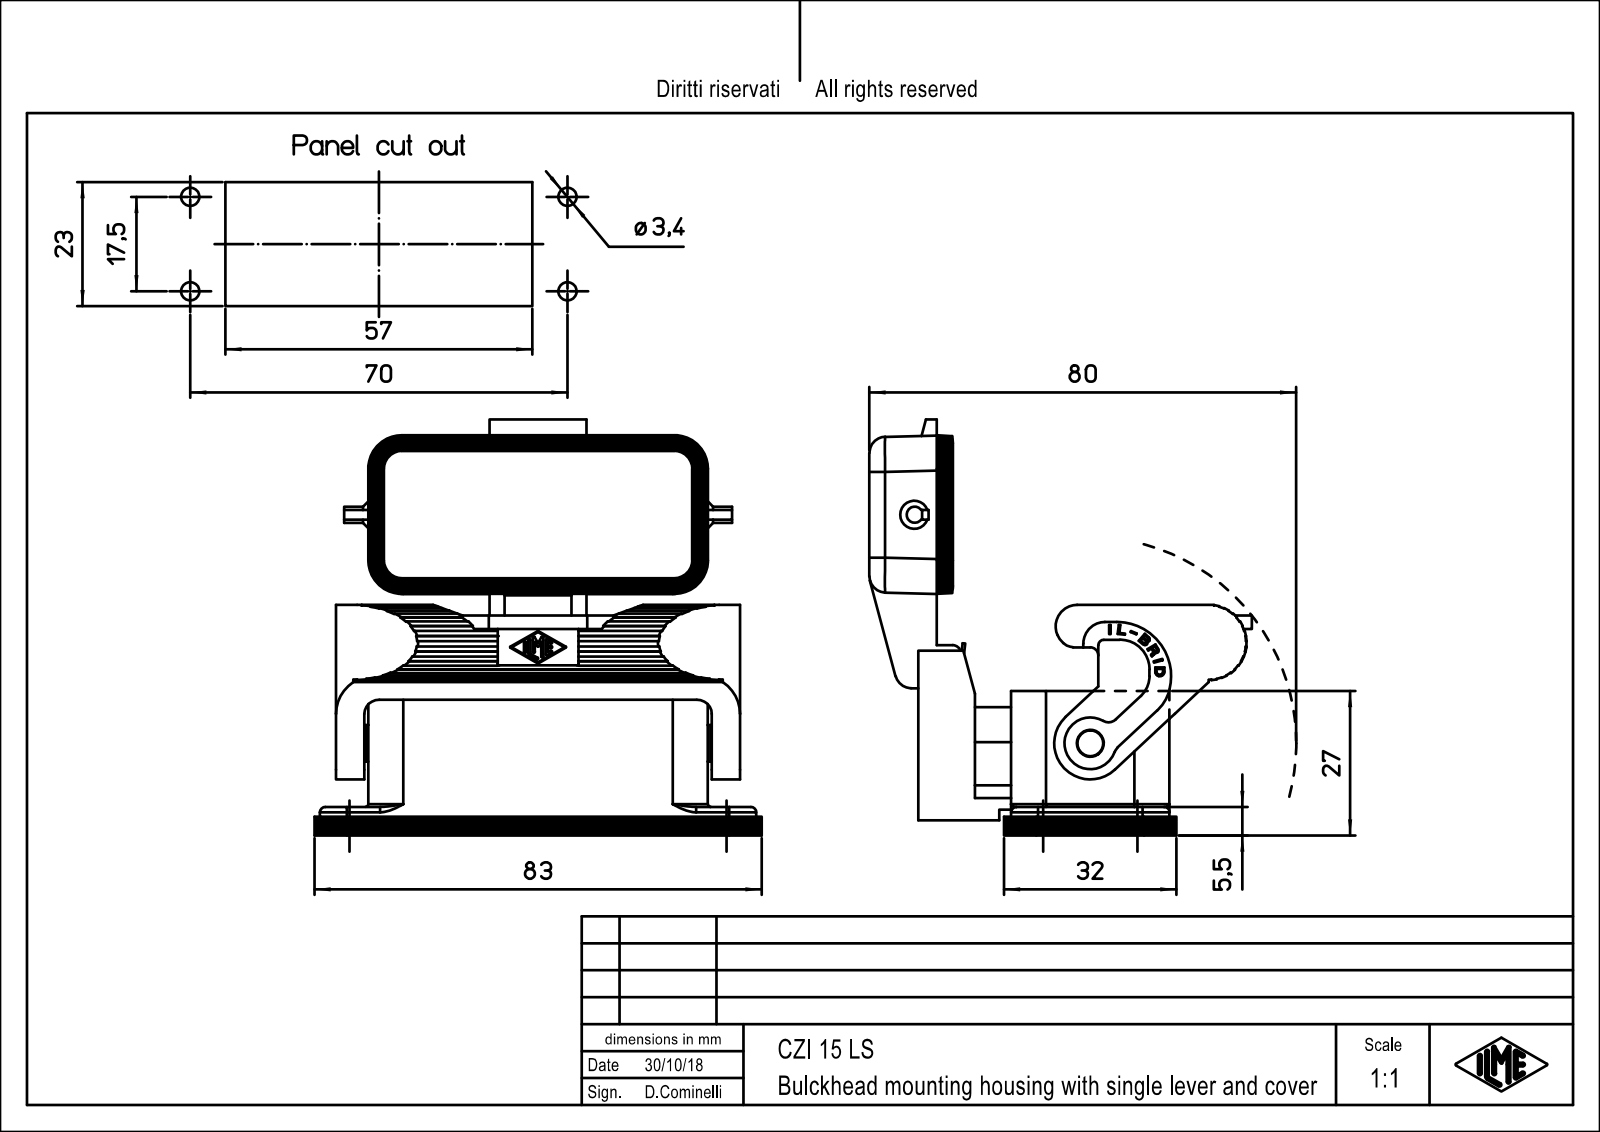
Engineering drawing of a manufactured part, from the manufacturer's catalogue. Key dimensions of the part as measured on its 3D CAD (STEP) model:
Part name (STEP PRODUCT): CZI_15_LS
STEP written by: PTC Creo Elements/Direct Modeling 19.0E 27-Jun-2016 (C) Parametric Technology GmbH (AUTOMOTIVE_DESIGN)
Units: millimetres
Bodies: 1 solid, 509 faces (274 planar, 195 cylindrical, 40 other)
Overall size (bounding box): 83 × 77.2 × 71
Volume: 50 203 mm³ · Surface area: 33 804 mm²
Round holes (diameter × count): ⌀2.8 ×4, ⌀3 ×4, ⌀3.4 ×4, ⌀5 ×1
Round bosses / shafts (diameter × count): ⌀7 ×1, ⌀6.8 ×1, ⌀4.8 ×1, ⌀3 ×1
Partial cylindrical surfaces — rounded edges, fillets, slot ends (radius × count): R0.2 ×15, R3 ×10, R3.5 ×8, R6 ×8, R6.5 ×8, R1 ×5, R5 ×5, R2.5 ×4
Main face-to-face distances: 2.76, 26.64, 2, 53.7, 55.7, 22.5, 6, 50.94, 52.94, 23.88
Hole centre spacings: 10.28, 19.64, 59.75, 62.05, 16, 17.5, 49.5, 52.02
